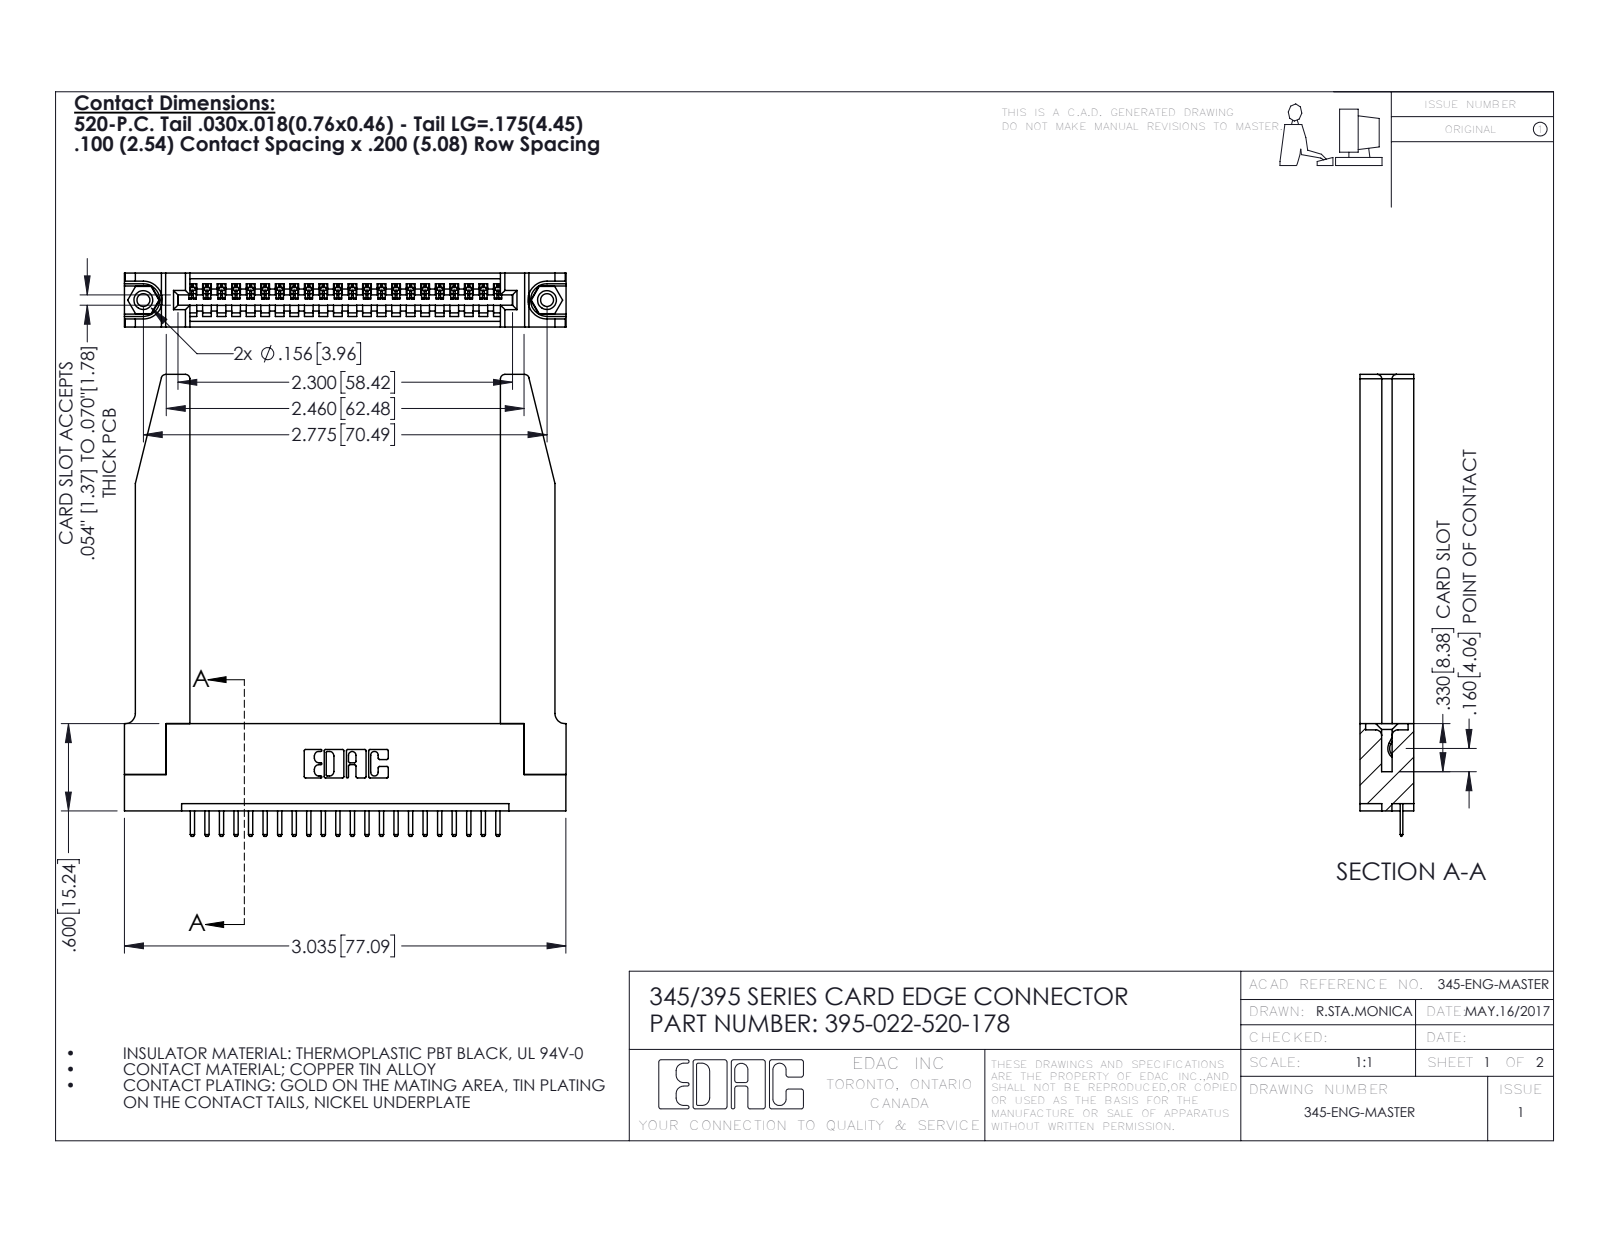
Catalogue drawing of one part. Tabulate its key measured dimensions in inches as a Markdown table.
| quantity | value |
| --- | --- |
| part name | 395-022-520-178; 345-292-001_345-293-120; 345-250-001_345-250-001-102; 345-220-078_345-220-078 (+1 more) |
| STEP written by | SolidWorks 2016 (CONFIG_CONTROL_DESIGN) |
| units | inches |
| bodies | 27 solids, 1724 faces (1146 planar, 526 cylindrical, 52 other) |
| overall size | 3.175 × 3.036 × 0.37 |
| volume | 0.907 in³ |
| surface area | 24.49 in² |
| round holes (diameter × count) | 0.089 × 2, 0.125 × 2, 0.156 × 2, 0.064 × 1 |
| round bosses / shafts (diameter × count) | 0.155 × 2 |
| partial cylindrical surfaces (radius × count) | 0.01 × 46, 0.006 × 44, 0.01 × 22, 0.03 × 8, 0.007 × 6, 0.031 × 6, 0.026 × 3, 0.031 × 2 |
| main face-to-face distances | 0.37, 0.072, 0.298, 0.2, 0.148, 0.15, 0.098, 0.272, 0.025, 0.077 |
| hole center spacings | 0.27, 2.541, 2.775 |
